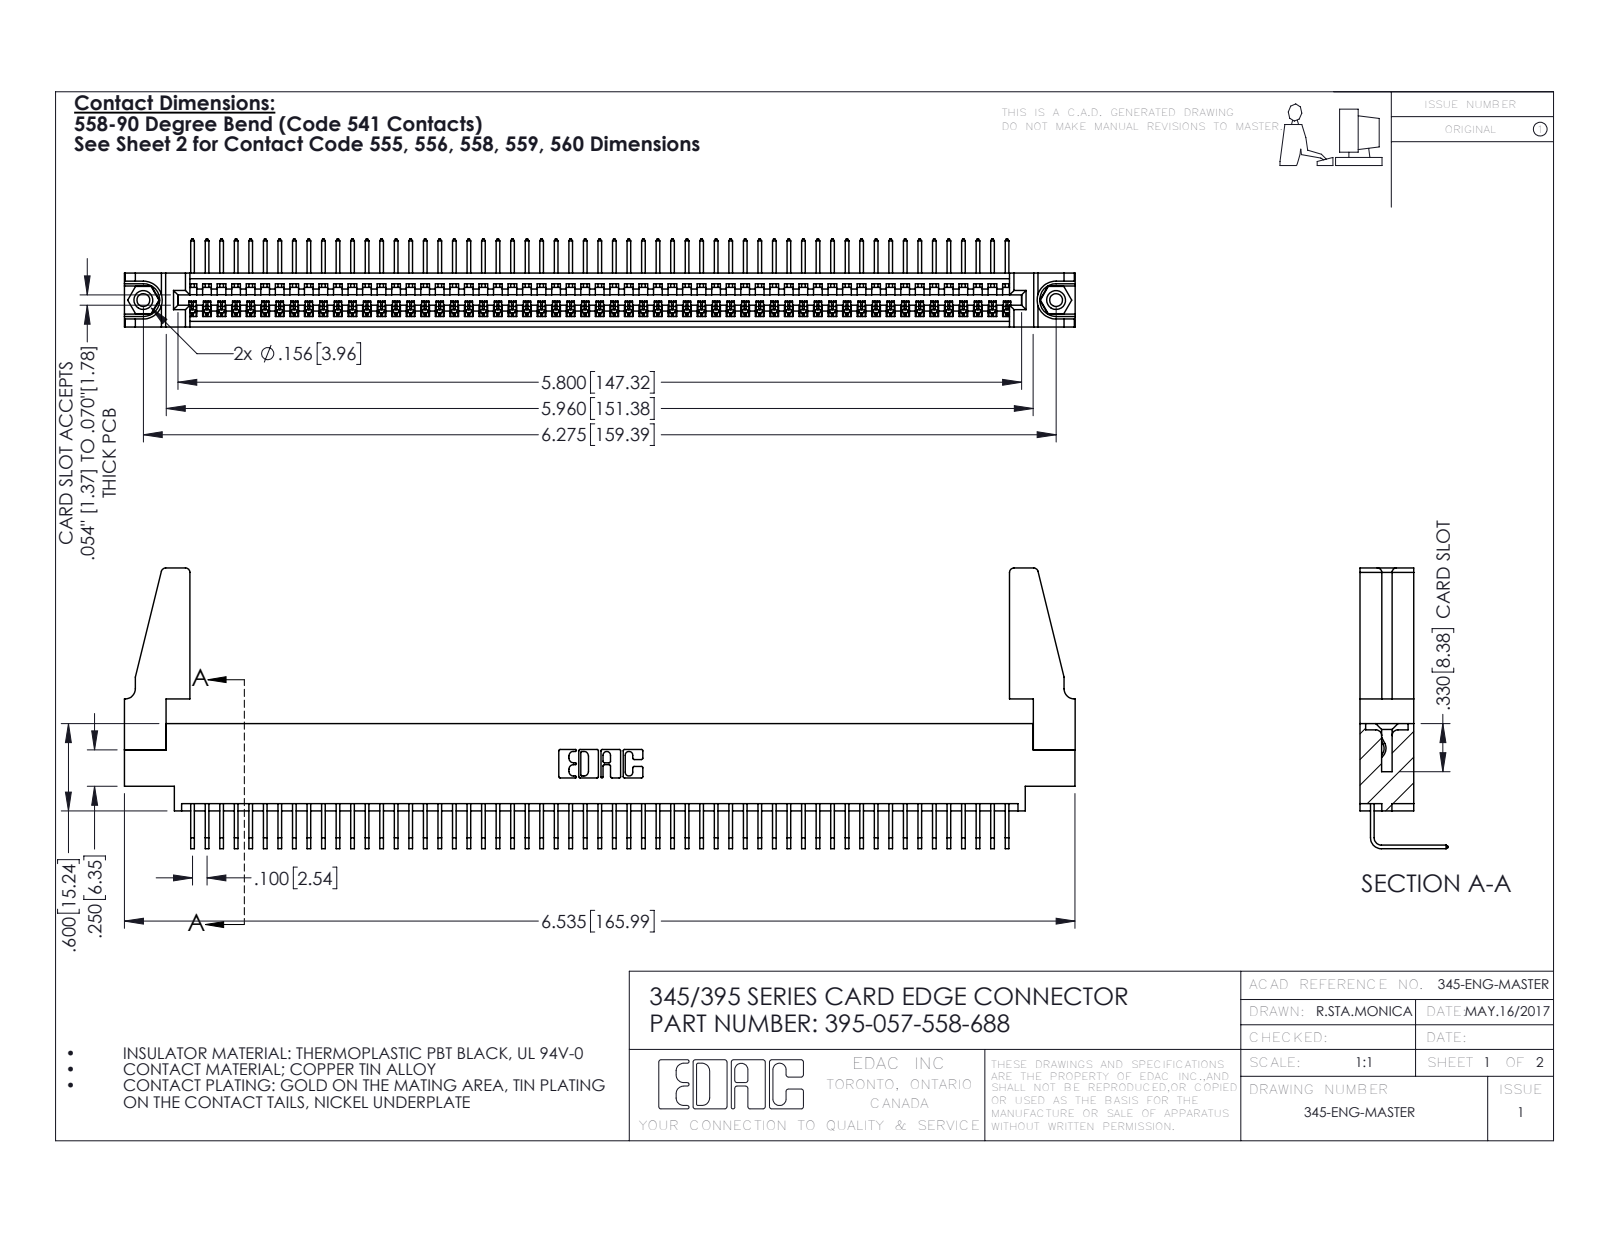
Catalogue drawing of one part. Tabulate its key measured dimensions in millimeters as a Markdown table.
| quantity | value |
| --- | --- |
| part name | 345-250-001_345-250-001-102; 345 Part_0.170 Offset - 0.156 Dia-TH; 395-057-558-688; 345-292-001_558 Tail - 2 (+1 more) |
| STEP written by | SolidWorks 2016 (CONFIG_CONTROL_DESIGN) |
| units | millimeters |
| bodies | 62 solids, 3674 faces (2550 planar, 1108 cylindrical, 16 other) |
| overall size | 166 × 49 × 15.4 |
| volume | 19 220 mm³ |
| surface area | 25 790 mm² |
| round holes (diameter × count) | 2.3 × 2, 3.2 × 2, 4 × 2, 1.6 × 1 |
| round bosses / shafts (diameter × count) | 3.9 × 2 |
| partial cylindrical surfaces (radius × count) | 0.2 × 114, 0.3 × 22, 0.8 × 8, 0.2 × 6, 0.8 × 6, 0.7 × 3, 0.8 × 2, 1 × 2 |
| main face-to-face distances | 1.8, 7.6, 9.4, 5.1, 2.5, 6.9, 0.6, 5.7, 4.4, 3.8 |
| hole center spacings | 6.9, 153.4, 159.4 |
